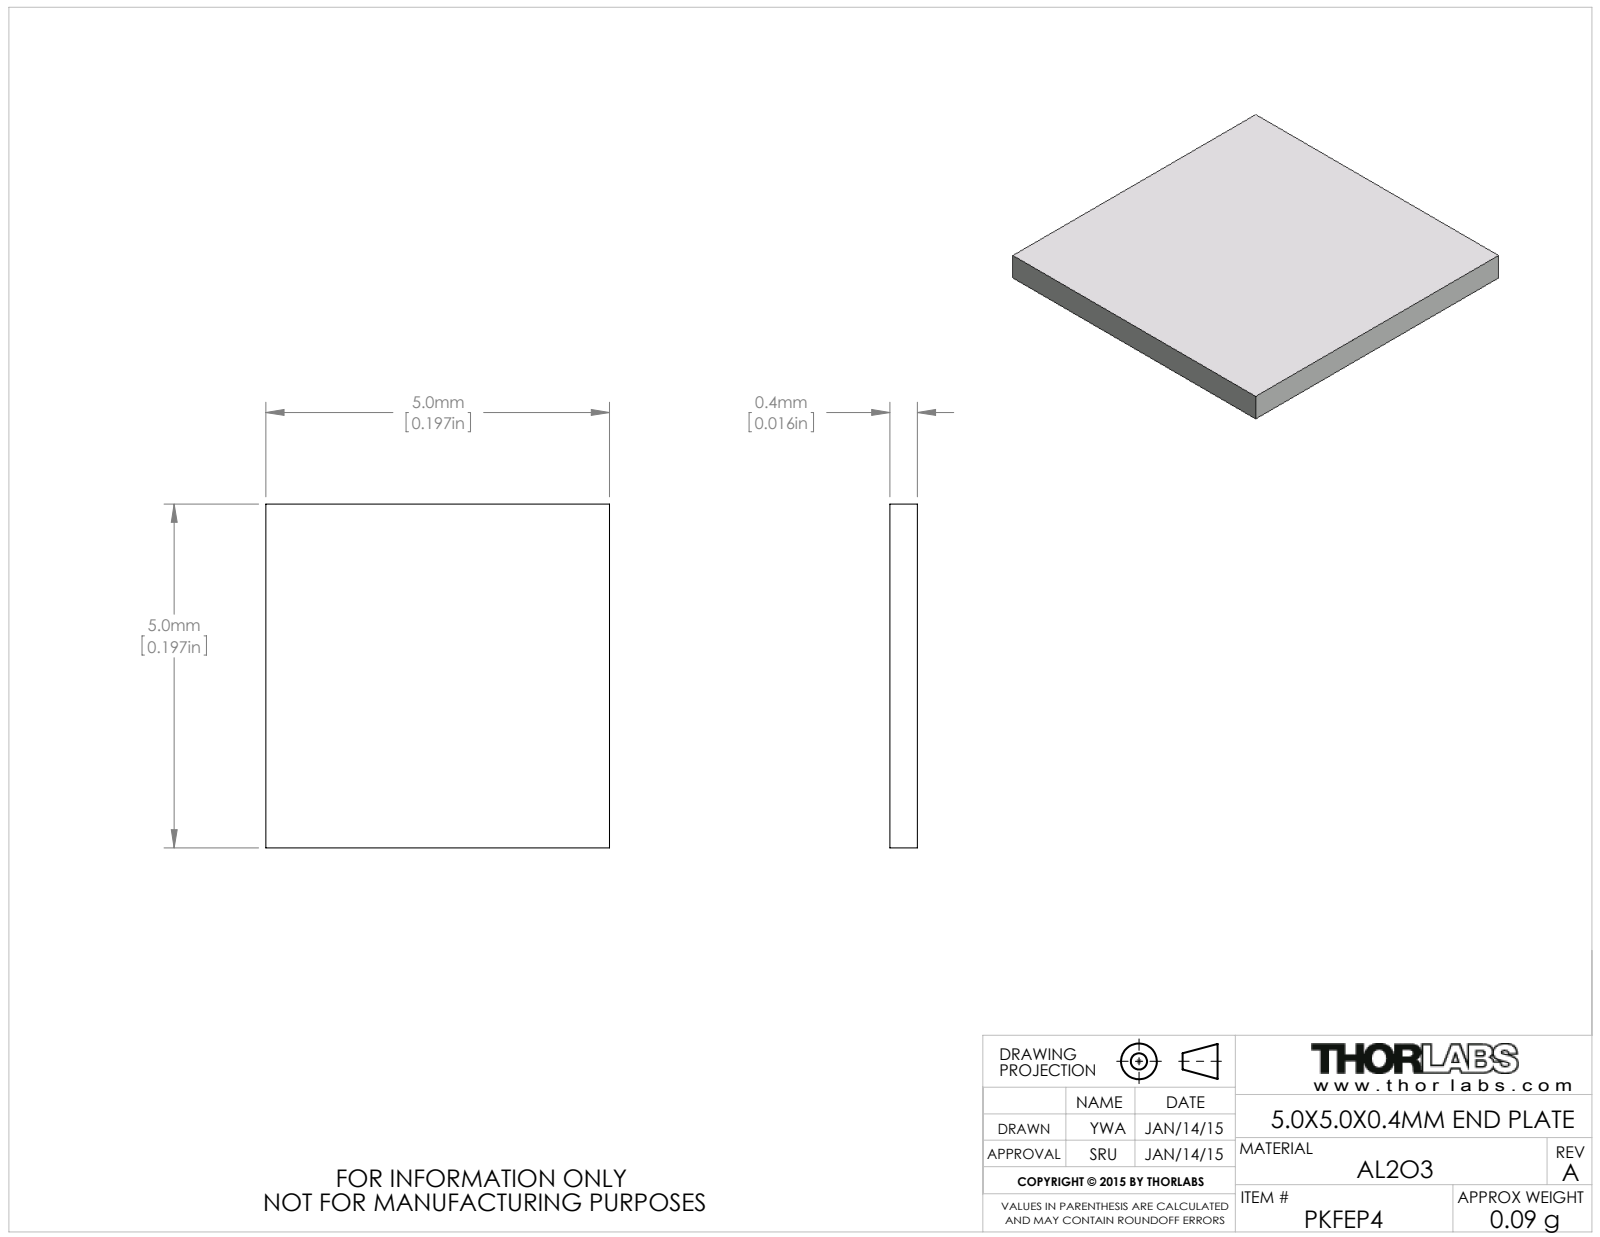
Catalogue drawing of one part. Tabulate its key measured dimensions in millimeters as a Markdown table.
| quantity | value |
| --- | --- |
| part name | PKFEP4 |
| STEP written by | SolidWorks 2012 (AUTOMOTIVE_DESIGN) |
| units | millimeters |
| bodies | 1 solid, 6 faces (6 planar, 0 cylindrical, 0 other) |
| overall size | 5 × 5 × 0.4 |
| volume | 10 mm³ |
| surface area | 58 mm² |
| main face-to-face distances | 0.4, 5 |
